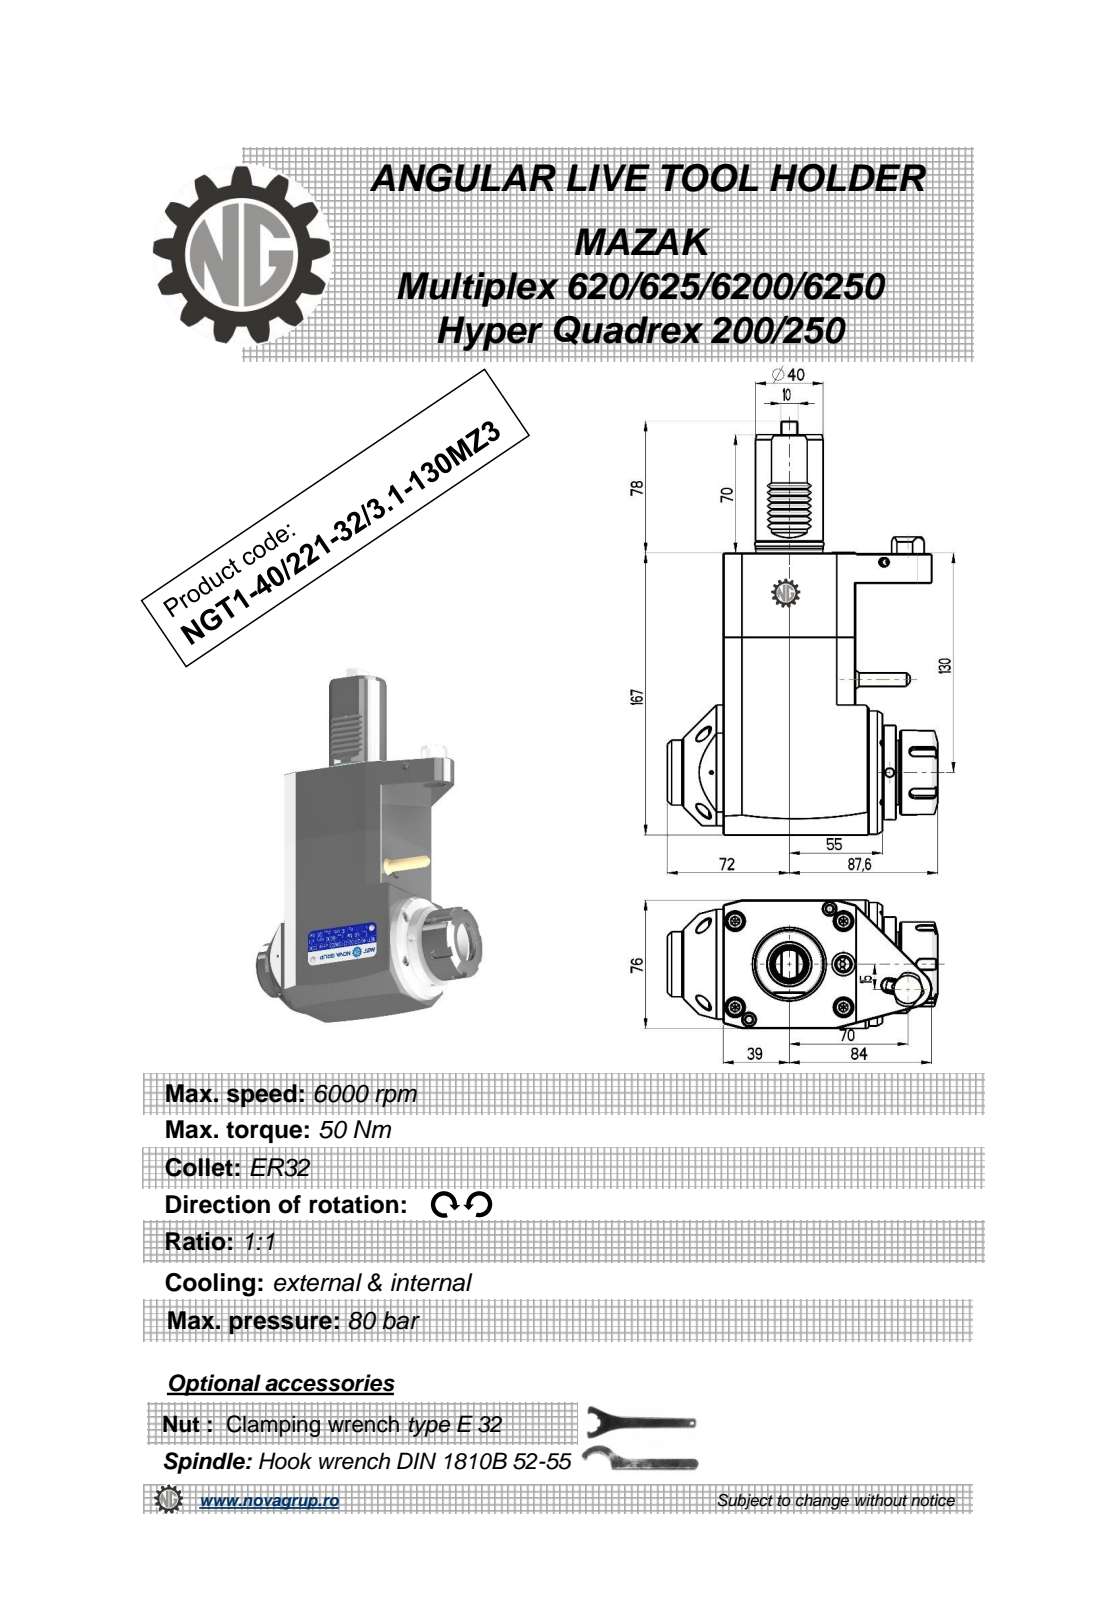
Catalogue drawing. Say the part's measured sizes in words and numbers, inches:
The part is named "NGT1_40_221_32_3_1_130MZ3". Its 3-D file was written by "PRO/ENGINEER BY PARAMETRIC TECHNOLOGY CORPORATION, 2010280 (CONFIG_CONTROL_DESIGN)". It is 1 solid with 293 faces: 136 planar, 72 cylindrical and 85 other. Overall it measures 9.646 by 6.283 by 2.992 inches. Its volume is 80.55 cubic inches and its surface area 142.3 square inches. Round holes: 1 of diameter 0.118, 1 of diameter 0.197, 1 of diameter 0.315, 1 of diameter 1.063. Round bosses or shafts: 2 of diameter 1.575, 1 of diameter 2.874, 1 of diameter 2.205, 1 of diameter 1.969, 1 of diameter 1.693, 1 of diameter 1.551, 1 of diameter 1.516, 1 of diameter 1.425. Partial cylindrical surfaces (rounded edges, fillets, slot ends): 7 of radius 0.012, 6 of radius 0.008, 5 of radius 0.118, 2 of radius 0.031, 2 of radius 0.098, 2 of radius 11.811, 1 of radius 0.354, 1 of radius 0.394. The main face-to-face distances are 2.992, 3.071, 6.575, 3.461, 0.709, 5.866, 0.315, 3.386, 0.433, 0.748. The hole center spacings are 2.379.
